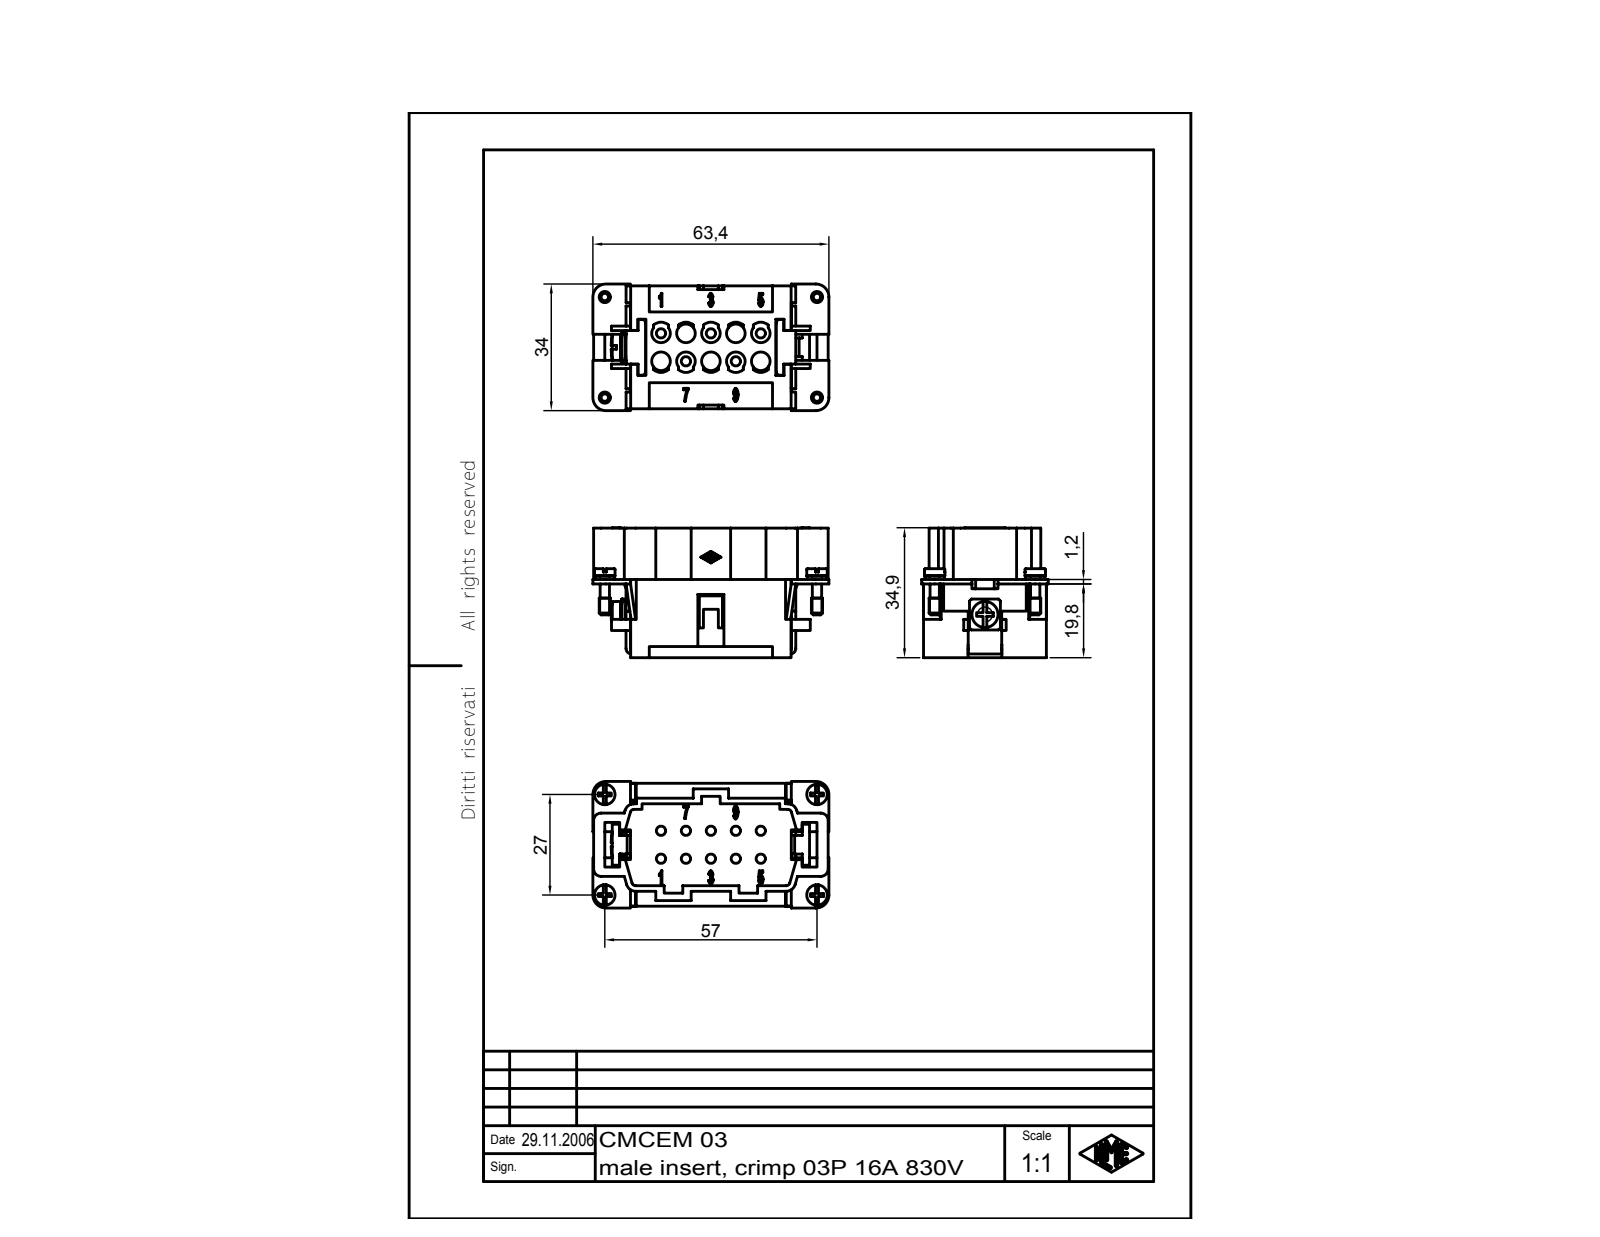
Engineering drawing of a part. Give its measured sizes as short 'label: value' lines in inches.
name: CMCEM 03
written by: Autodesk Inventor 7 (AUTOMOTIVE_DESIGN)
unit: in
bodies: 1 solid, 770 faces (355 planar, 105 cylindrical, 310 other)
size: 2.496 × 1.374 × 1.339
volume: 2.037 in³; area: 29.54 in²
holes: 5× ⌀0.098, 2× ⌀0.1, 2× ⌀0.197, 1× ⌀0.128, 1× ⌀0.276
bosses: 2× ⌀0.217, 2× ⌀0.209, 2× ⌀0.118, 2× ⌀0.098
rounds: 14× R0.004, 10× R0.098, 6× R0.039, 6× R0.079, 5× R0.118, 2× R0.059, 2× R0.138, 1× R0.217
face distances: 0.059, 0.157, 0.866, 1.083, 0.118, 0.098, 0.217, 0.827, 0.925, 0.039
hole spacings: 0.264, 0.396, 0.528, 0.295, 0.605, 0.791, 0.844, 0.94
